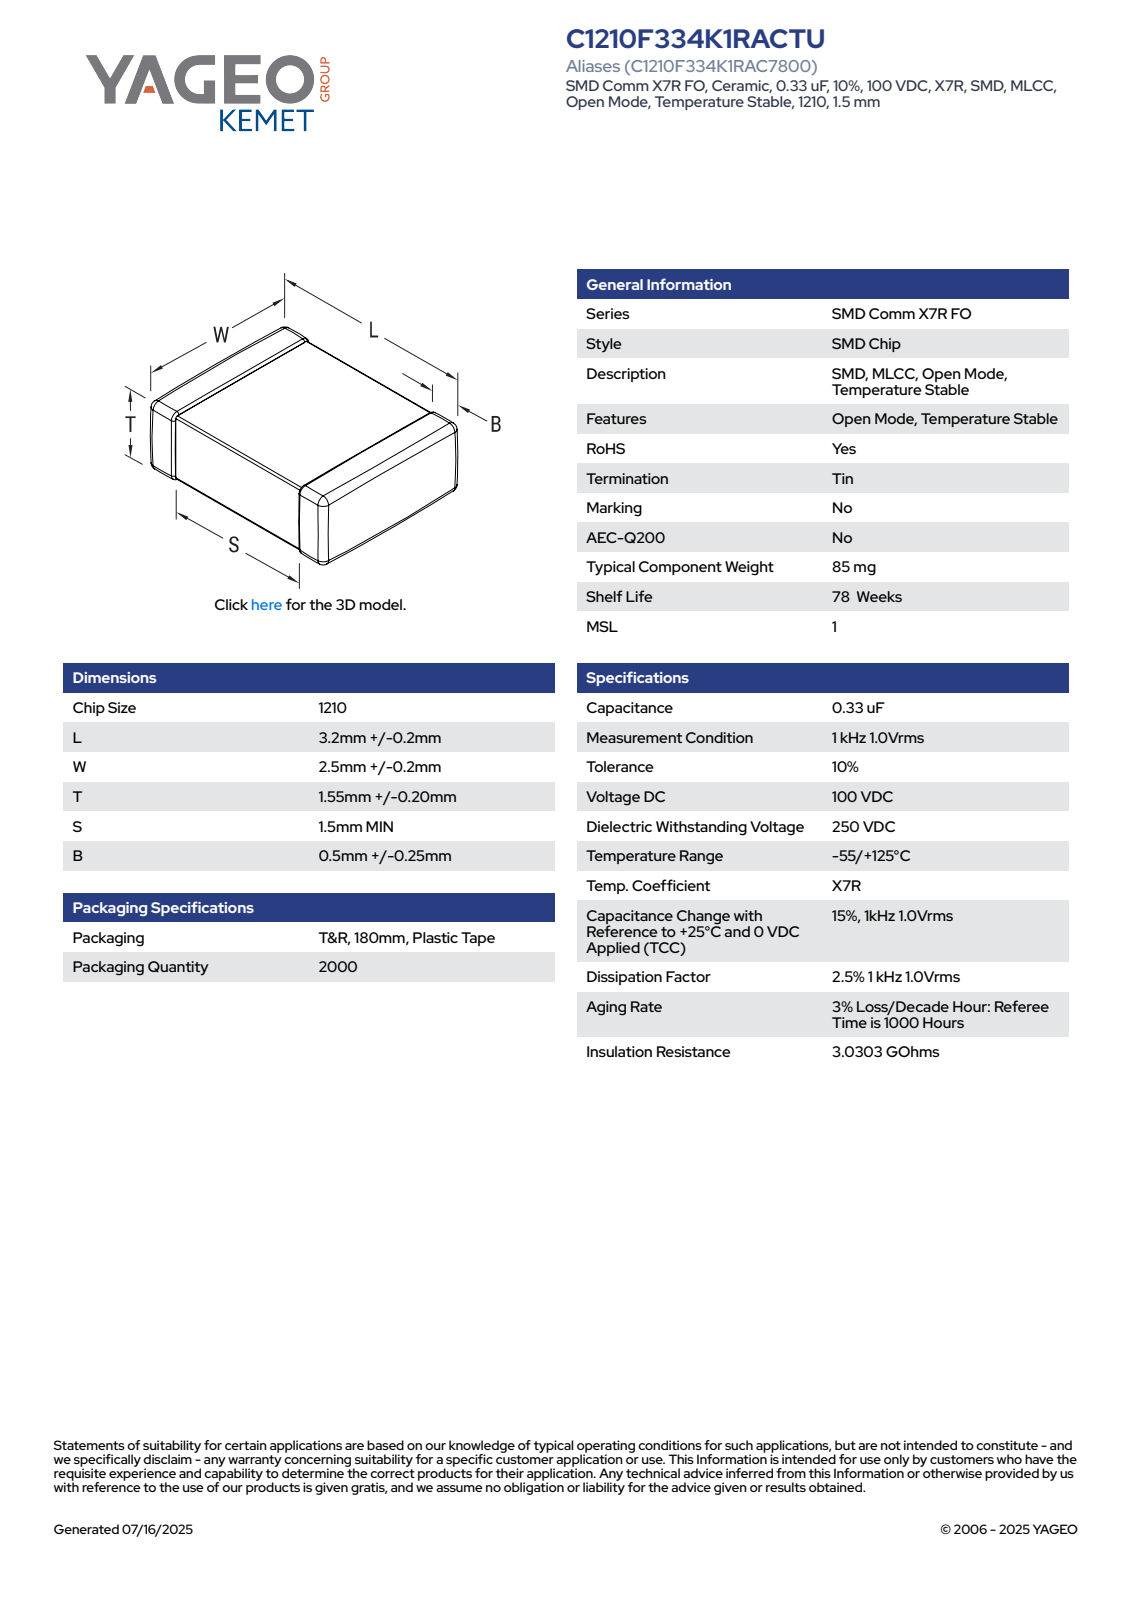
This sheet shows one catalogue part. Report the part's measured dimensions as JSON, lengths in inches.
{"part_name": "CCS_CCSTD_1210_L3.4W2.7T1.75B0.5", "step_written_by": "SolidWorks 2021 (AUTOMOTIVE_DESIGN)", "units": "inches", "bodies": {"solids": 4, "faces": 125, "planar": 71, "cylindrical": 38, "other": 16}, "overall_size": [0.134, 0.106, 0.069], "volume_in3": 0.001, "surface_area_in2": 0.062, "face_to_face_distances": [0.067, 0.064, 0.134, 0.104, 0.069, 0.102, 0.106, 0.065, 0.067, 0.016]}
